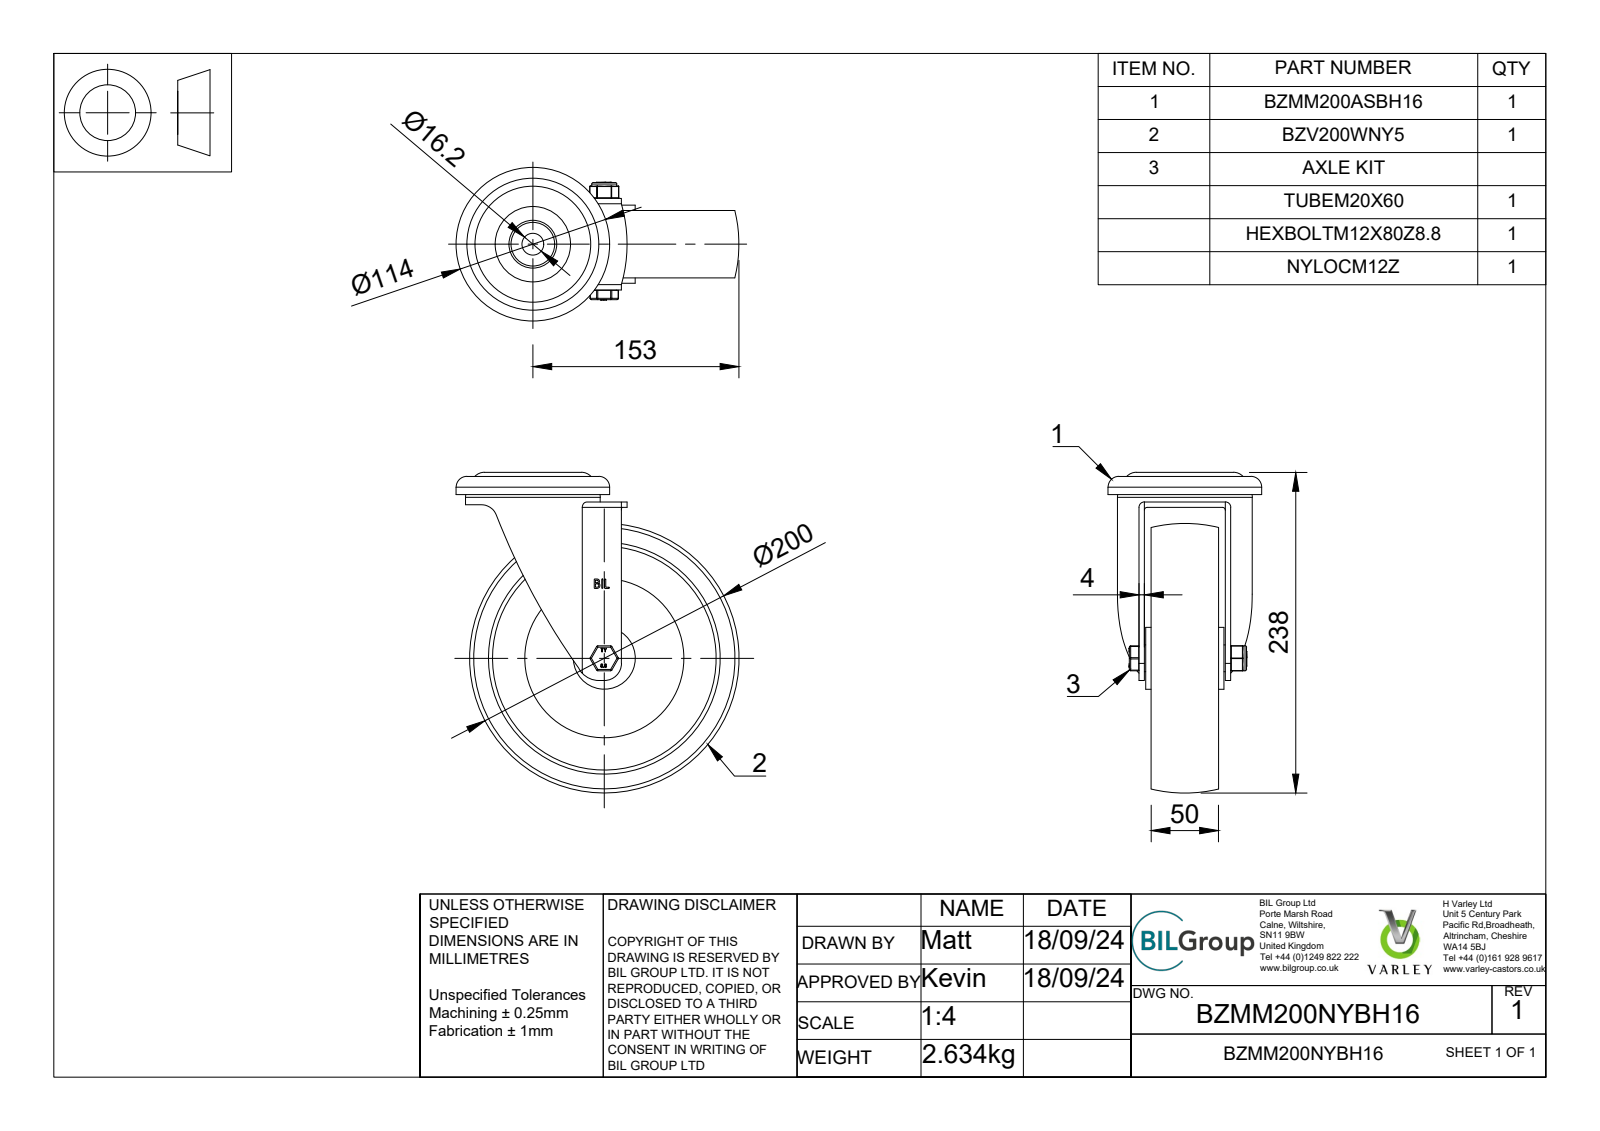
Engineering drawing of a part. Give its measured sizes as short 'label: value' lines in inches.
name: BZMM200NYBH16 v3; BZMM200ASBH16 v1; ZINC PLATED, PRESSED STEEL HEAD; ZINC PLATED, PRESSED STEEL FORKS (+8 more)
written by: Autodesk Translation Framework v13.20.0.188 (AUTOMOTIVE_DESIGN)
unit: in
bodies: 7 solids, 368 faces (160 planar, 113 cylindrical, 95 other)
size: 9.37 × 8.268 × 4.488
volume: 60.33 in³; area: 354.6 in²
holes: 1× ⌀0.472, 1× ⌀0.48, 1× ⌀0.492, 1× ⌀0.551, 1× ⌀0.638, 1× ⌀0.795, 1× ⌀1.614, 1× ⌀2.047, 1× ⌀3.622, 1× ⌀4.094, 1× ⌀6.772
bosses: 1× ⌀4.488, 1× ⌀3.937, 1× ⌀2.913, 1× ⌀1.85, 1× ⌀1.811, 1× ⌀1.28, 1× ⌀0.783, 1× ⌀0.728
rounds: 18× R0.02, 12× R0.039, 4× R0.079, 2× R0.157, 1× R0.472, 1× R0.502, 1× R0.659, 1× R4.252
face distances: 0.738, 1.23, 0.197, 0.157, 0.492, 2.323, 0.354, 1.585, 1.093, 2.52
